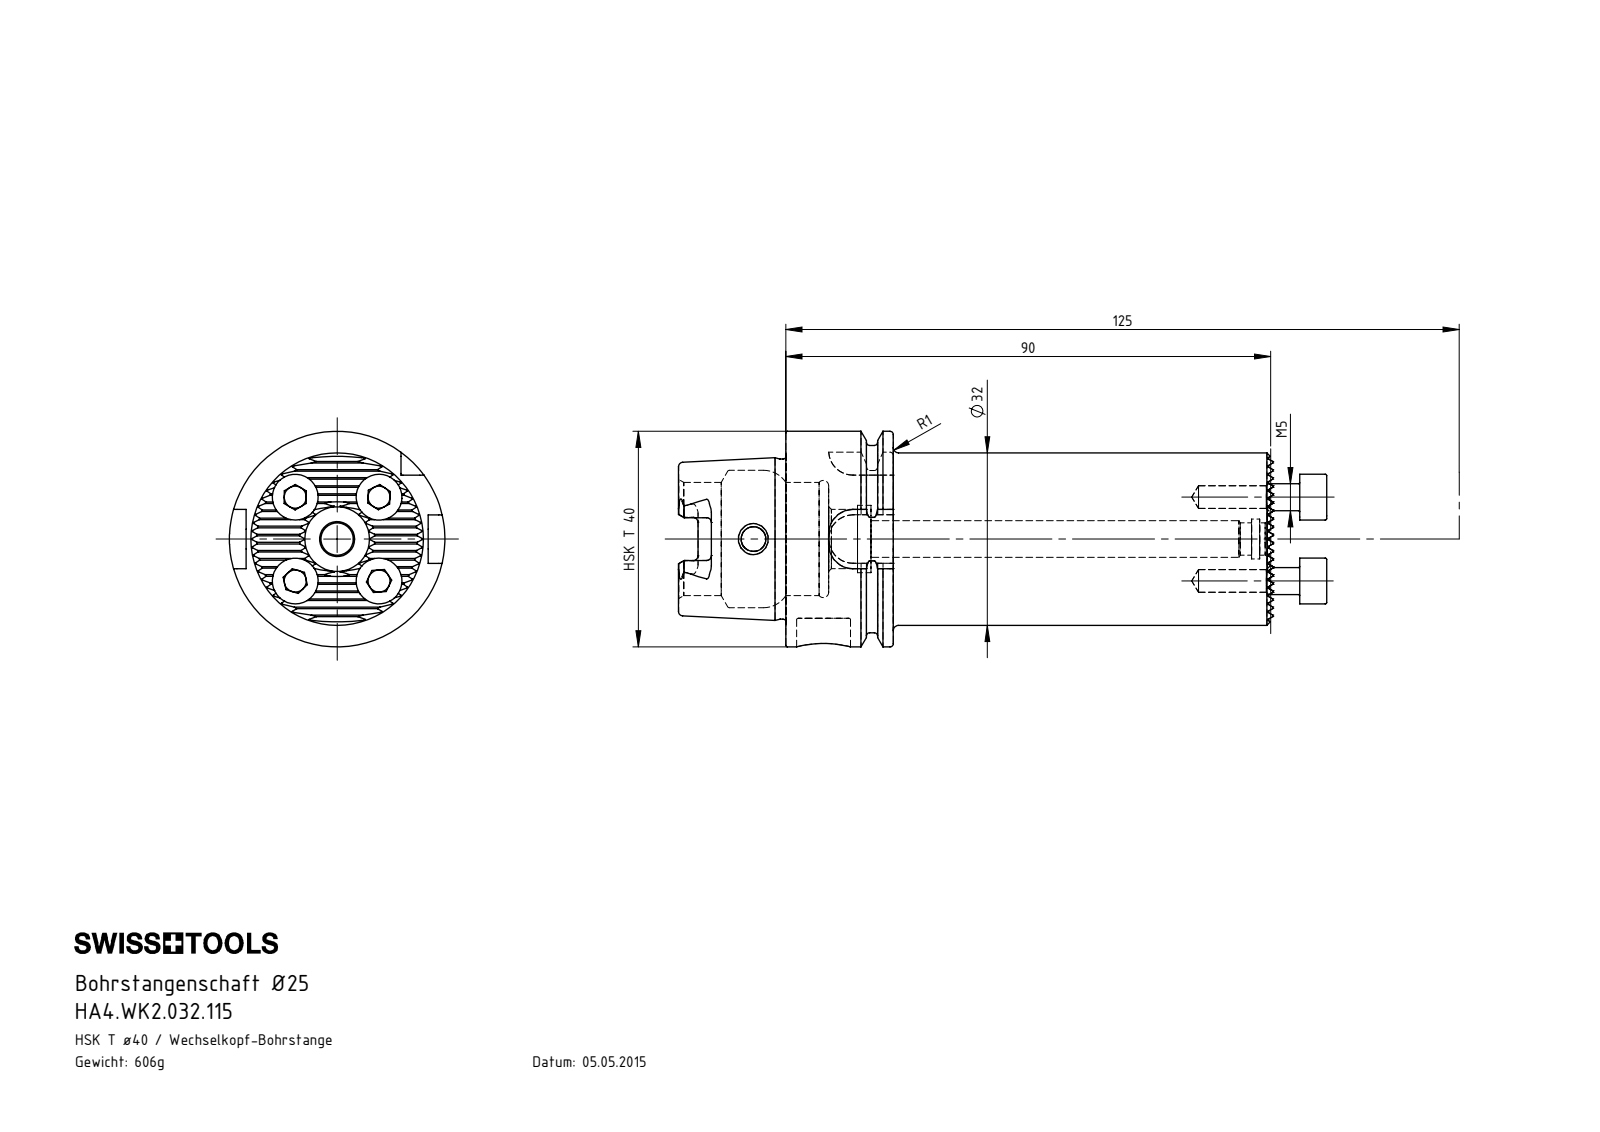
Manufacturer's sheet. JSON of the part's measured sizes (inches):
{"part_name": "DIN 3771 - 6x1; HA4-WK2.032.115_A; ISO 4762 - M5 x 14; HA4.WK2.032.115", "step_written_by": "SolidWorks 2017 (AUTOMOTIVE_DESIGN)", "units": "inches", "bodies": {"solids": 5, "faces": 450, "planar": 223, "cylindrical": 114, "other": 113}, "overall_size": [4.343, 1.575, 1.575], "volume_in3": 4.379, "surface_area_in2": 29.63, "round_holes": [[0.165, 4], [0.181, 1], [0.197, 1], [0.236, 1], [0.291, 1], [0.394, 1], [0.433, 1], [0.492, 1], [0.827, 1], [1.004, 1]], "round_bosses_or_shafts": [[0.335, 3], [0.197, 3], [1.575, 1], [1.368, 1], [1.26, 1], [1.17, 1]], "partial_cylinders_radius": [[0.005, 21], [0.035, 6], [0.074, 4], [0.177, 4]], "face_to_face_distances": [0.051, 0.102, 0.154, 0.205, 0.511, 0.256, 0.46, 0.563, 0.409, 0.307], "hole_center_spacings": [0.433, 0.613, 0.867]}
